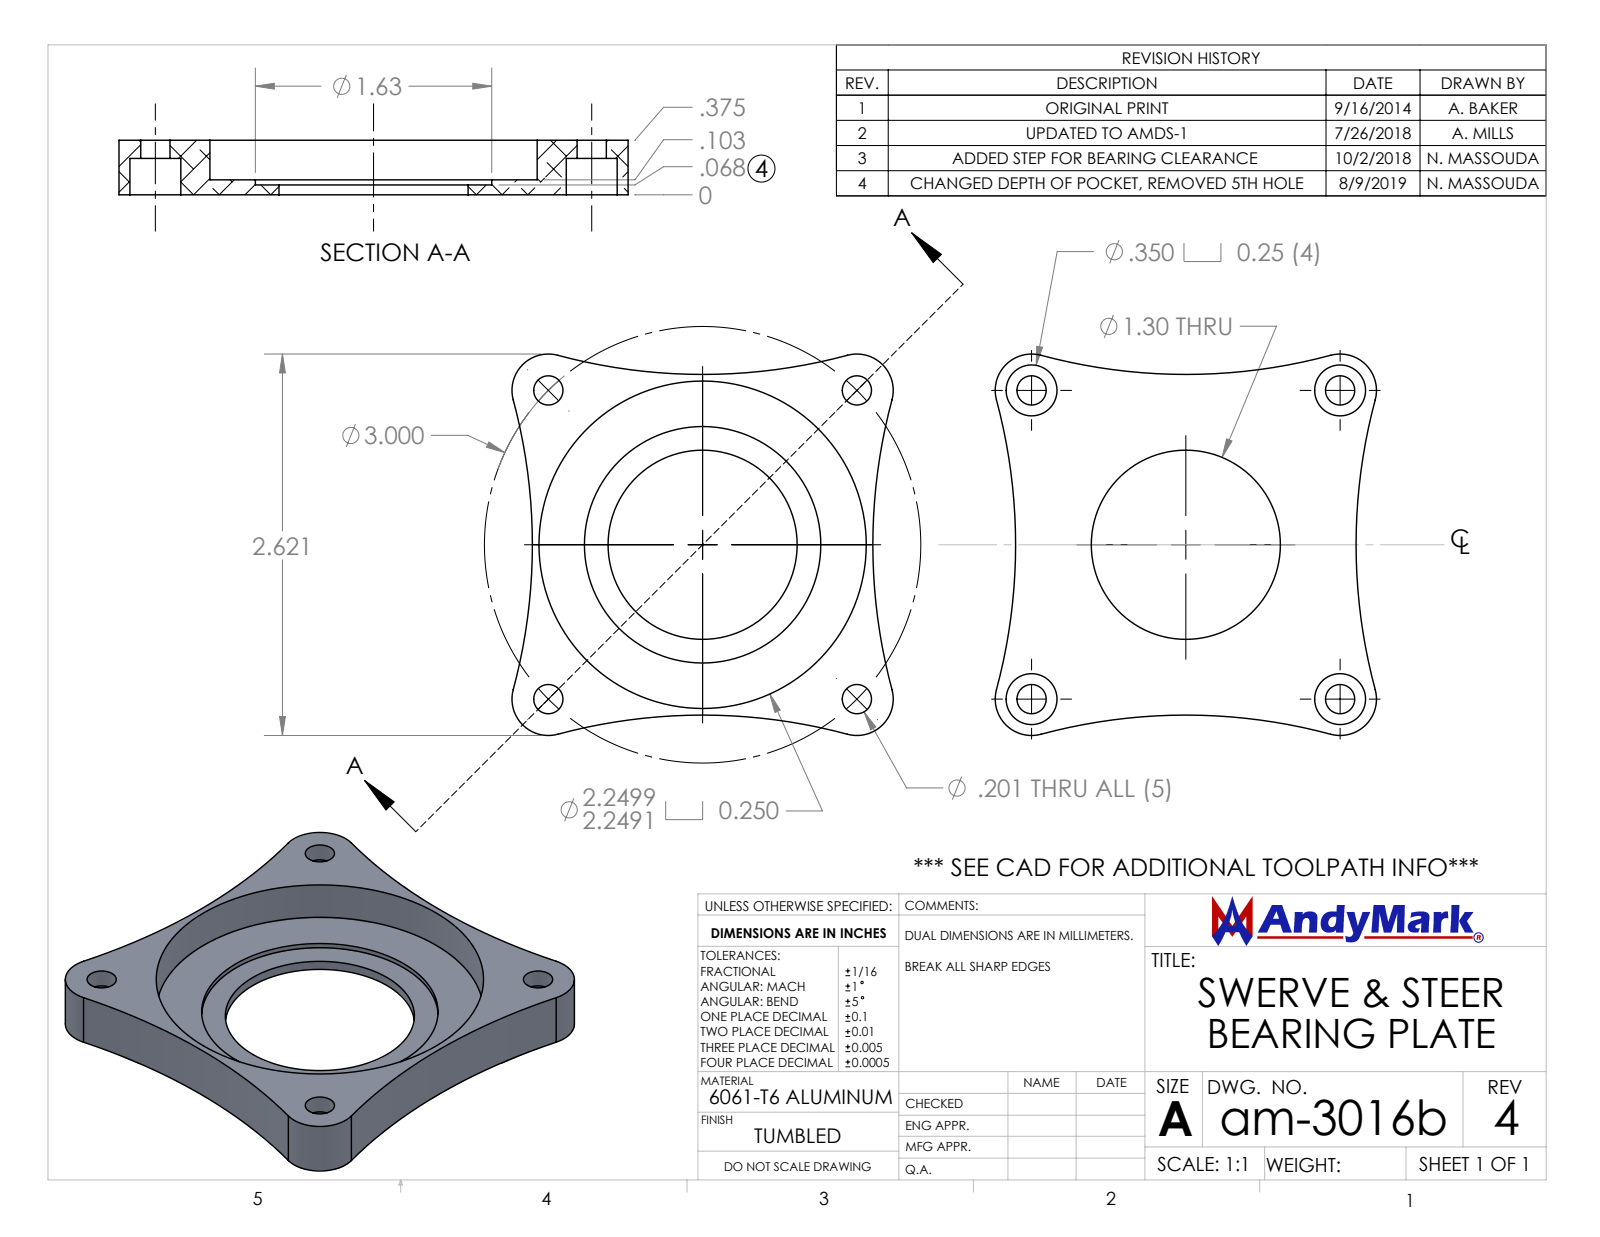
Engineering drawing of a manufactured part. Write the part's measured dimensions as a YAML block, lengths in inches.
part_name: "am-3016b S&S Bearing Plate"
step_written_by: "SolidWorks 2019 (CONFIG_CONTROL_DESIGN)"
units: inches
bodies: {solids: 1, faces: 41, planar: 8, cylindrical: 33, other: 0}
overall_size: [2.621, 2.621, 0.375]
volume: 0.91
surface_area: 16.79
round_holes:
  - {diameter: 0.201, count: 4}
  - {diameter: 0.35, count: 4}
  - {diameter: 1.3, count: 1}
  - {diameter: 1.625, count: 1}
  - {diameter: 2.25, count: 1}
partial_cylinders:
  - {radius: 0.25, count: 4}
  - {radius: 3.83, count: 4}
face_to_face_distances: [0.375, 0.103, 0.272, 0.068, 0.035, 0.307, 0.25, 0.182, 0.147, 0.125]
hole_center_spacings: [1.5, 2.121, 3]
